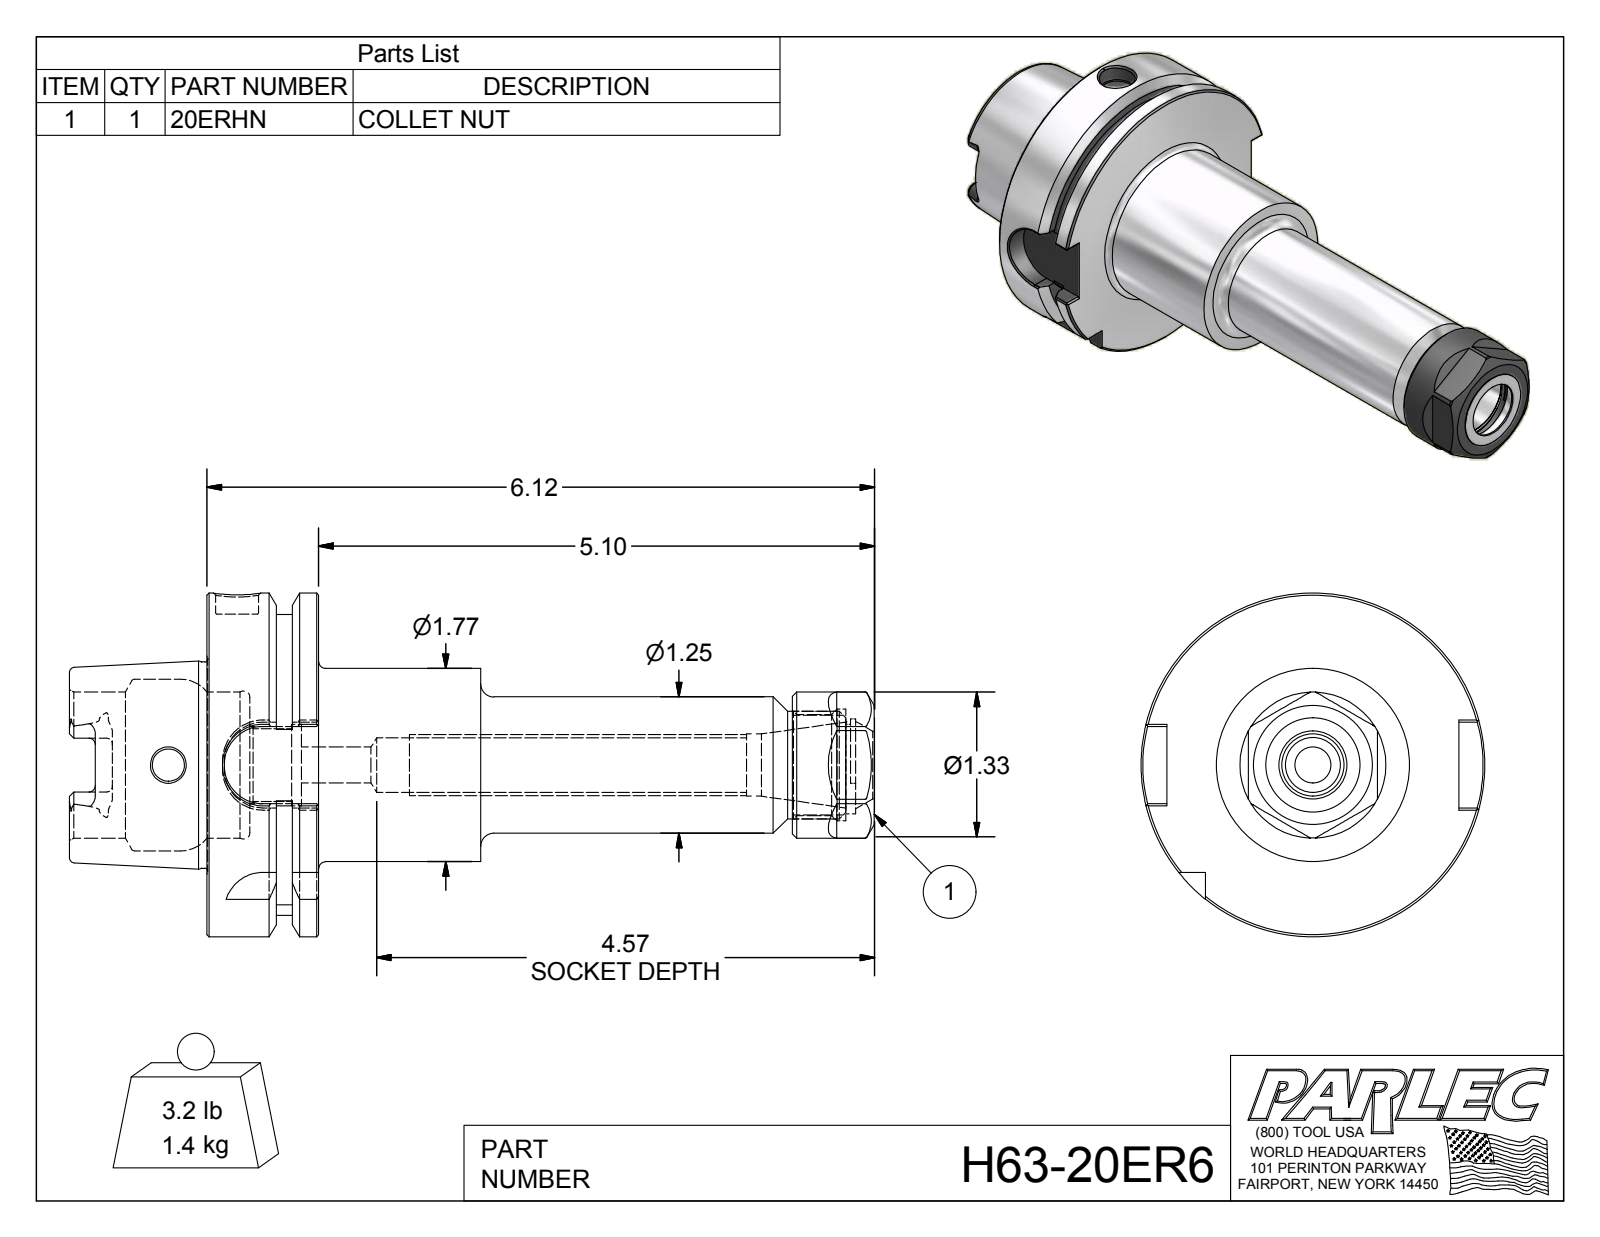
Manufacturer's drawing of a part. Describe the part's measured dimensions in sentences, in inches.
The part is named "H63-20ER6; H63-20ER6-1; 20ERHN". Its 3-D file was written by "Autodesk Inventor 2012 (AUTOMOTIVE_DESIGN)". It is 2 solids with 180 faces: 74 planar, 44 cylindrical and 62 other. Overall it measures 7.38 by 3.15 by 3.15 inches. Its volume is 14.75 cubic inches and its surface area 78.61 square inches. Round holes: 1 of diameter 0.295, 1 of diameter 0.33, 1 of diameter 0.331, 1 of diameter 0.394, 1 of diameter 0.502, 1 of diameter 0.57, 1 of diameter 0.62, 1 of diameter 0.666, 1 of diameter 0.749, 1 of diameter 0.82, 1 of diameter 0.925, 1 of diameter 1.024. Round bosses or shafts: 1 of diameter 3.15, 1 of diameter 1.891, 1 of diameter 1.77, 1 of diameter 1.25, 1 of diameter 0.984, 1 of diameter 0.86. Partial cylindrical surfaces (rounded edges, fillets, slot ends): 6 of radius 0.059, 4 of radius 0.113, 4 of radius 0.354, 1 of radius 0.423, 1 of radius 1.378. The main face-to-face distances are 1.024, 0.394, 0.63, 0.748, 0.782, 0.389, 0.241, 0.635, 0.241, 0.148. The hole center spacings are 0.037.
